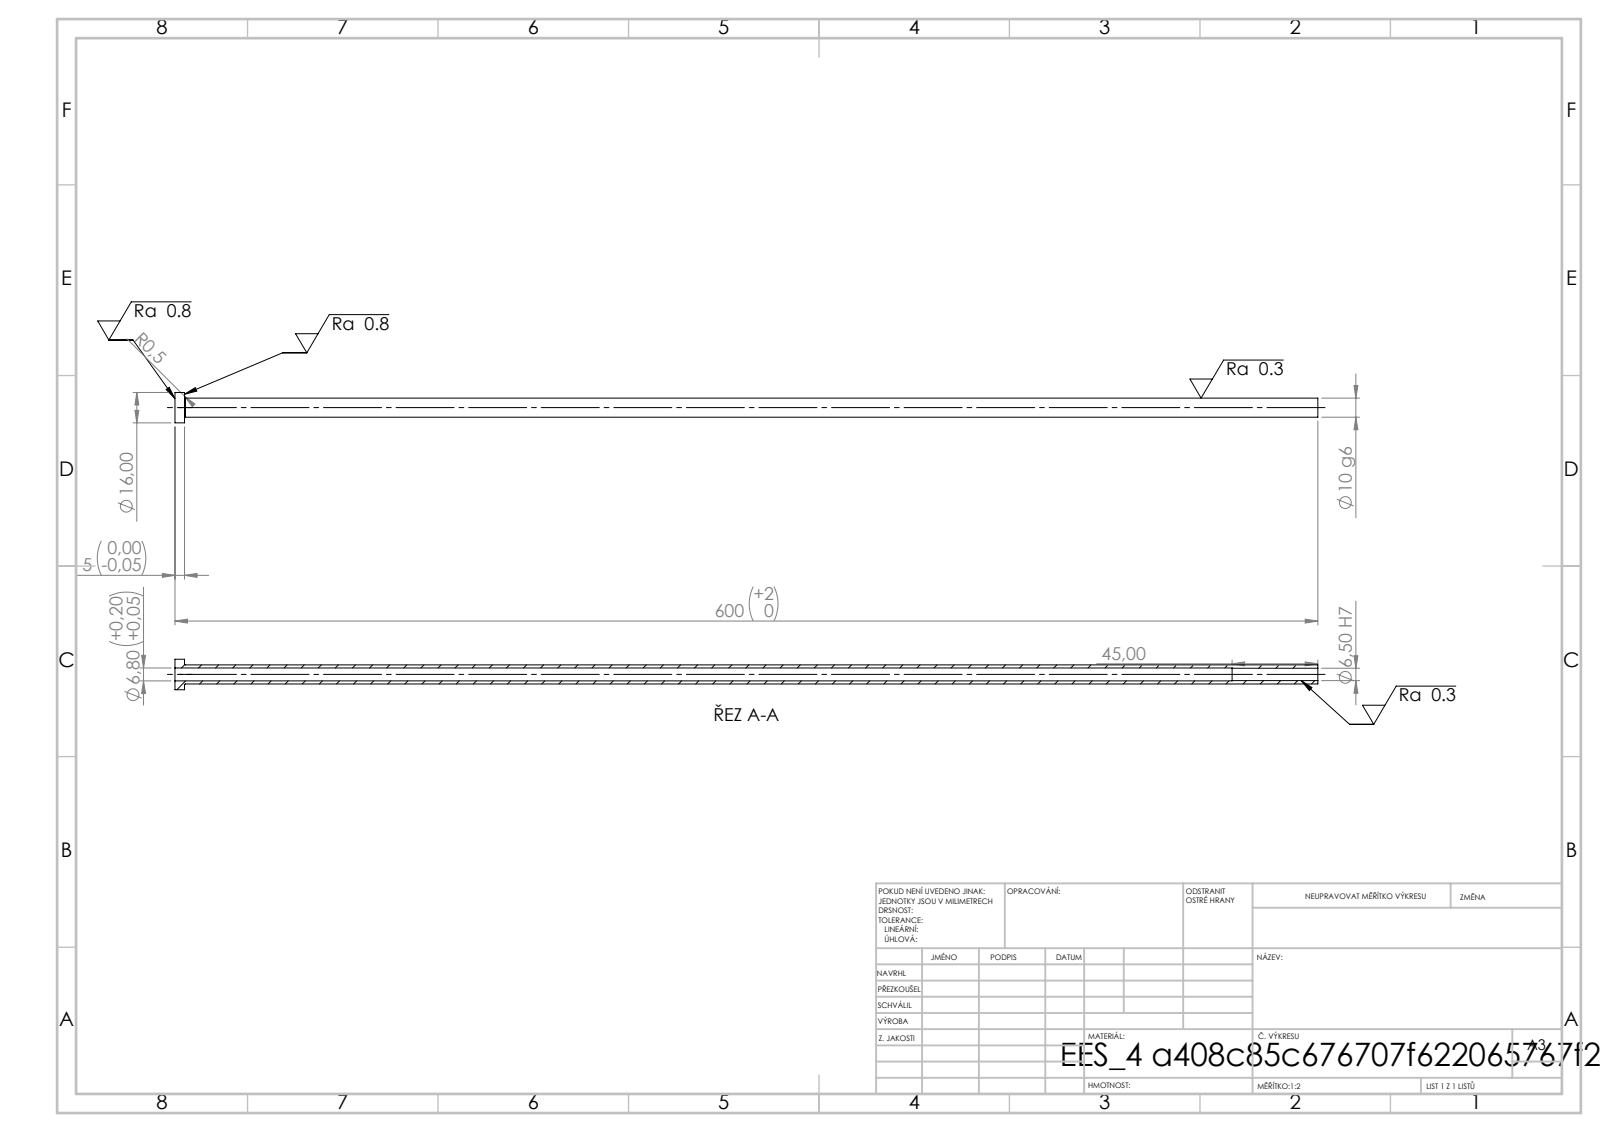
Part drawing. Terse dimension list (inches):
written by: SolidWorks 2019 (CONFIG_CONTROL_DESIGN)
unit: in
bodies: 1 solid, 14 faces (4 planar, 8 cylindrical, 2 other)
size: 23.622 × 0.63 × 0.63
volume: 1.592 in³; area: 49.67 in²
holes: 1× ⌀0.256, 1× ⌀0.268
bosses: 1× ⌀0.63, 1× ⌀0.394
face distances: 0.197, 23.622, 23.425, 21.85, 21.654, 1.772
